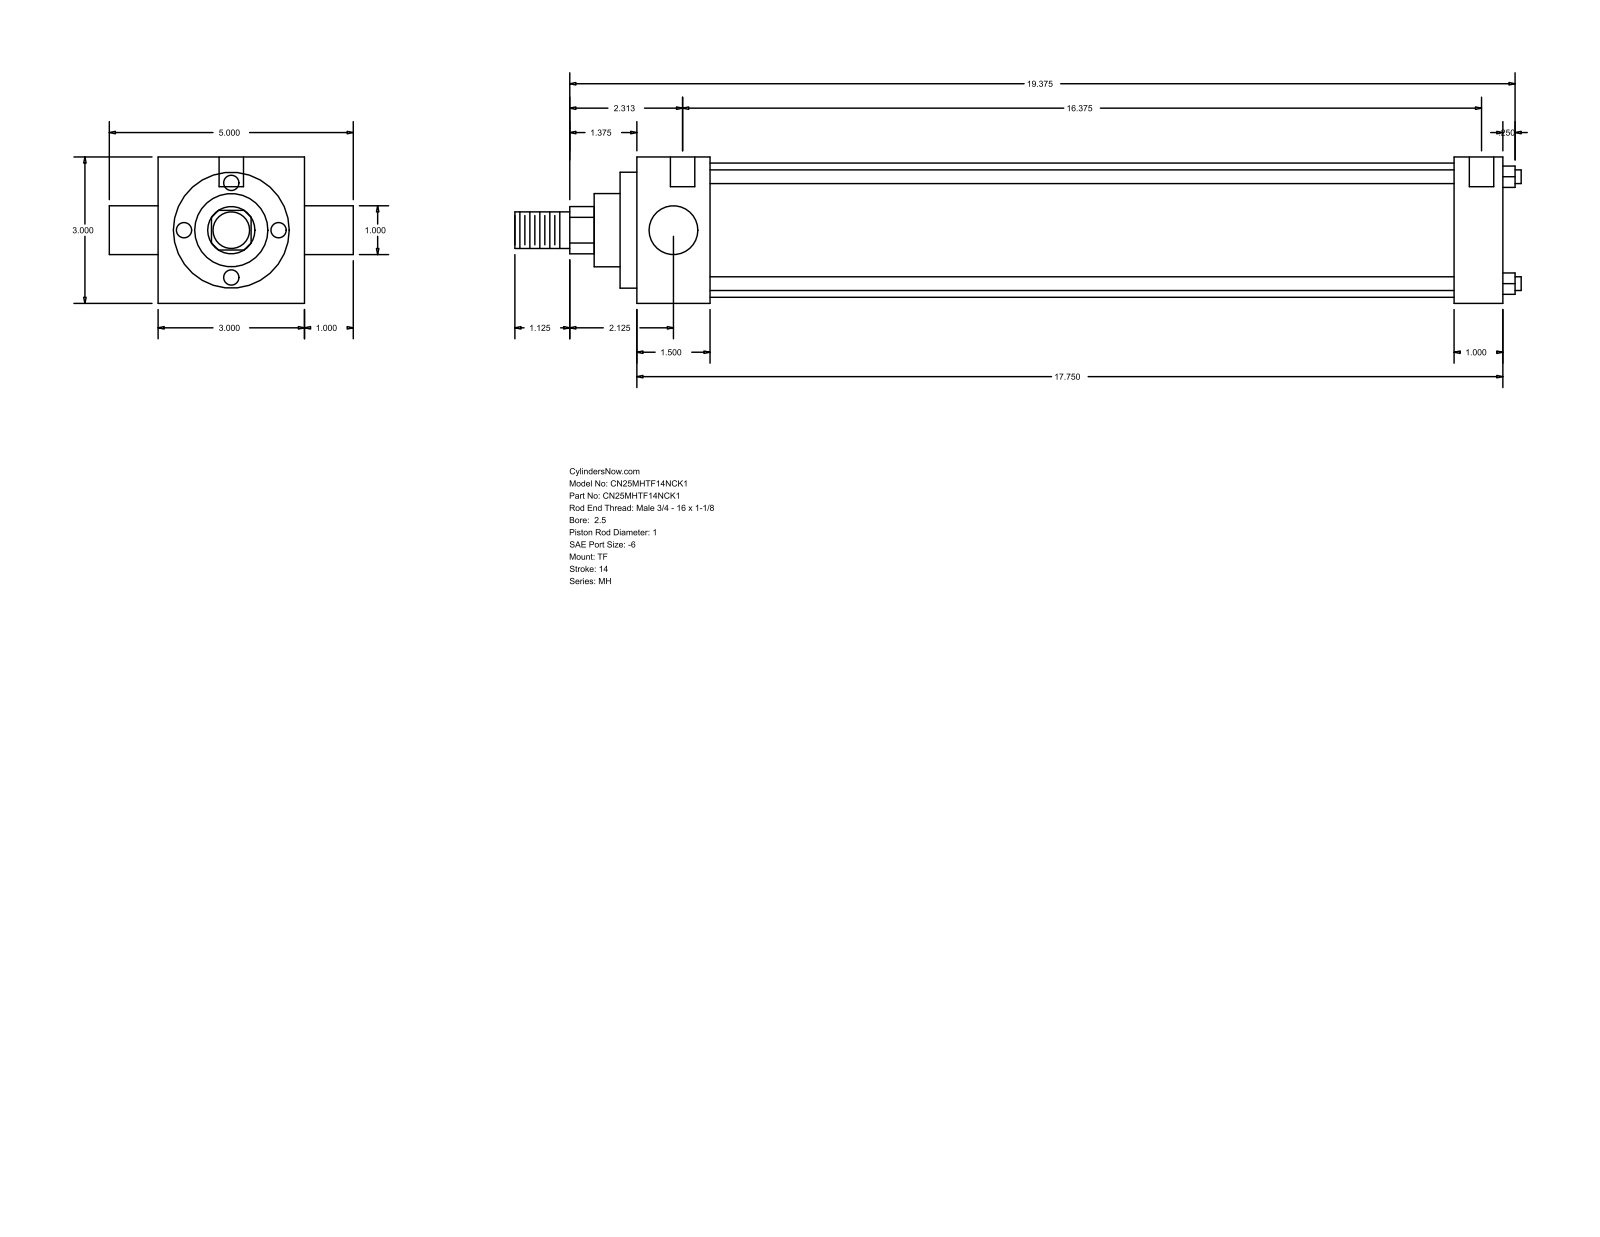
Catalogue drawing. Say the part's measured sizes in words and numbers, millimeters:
The part is named "MH_TF__0250_1". Its 3-D file was written by "GSSL Pune (CONFIG_CONTROL_DESIGN)". It is 0 solids with 86 faces: 61 planar, 25 cylindrical and 0 other. Overall it measures 523.88 by 127 by 76.2 millimeters. Round holes: 3 of diameter 5.56, 2 of diameter 12.7. Round bosses or shafts: 4 of diameter 7.14, 2 of diameter 25.4, 1 of diameter 69.85, 1 of diameter 60.33, 1 of diameter 38.1, 1 of diameter 19.05. Partial cylindrical surfaces (rounded edges, fillets, slot ends): 1 of radius 12.29. The main face-to-face distances are 76.2, 450.85, 25.39, 38.11, 412.74, 425.46, 387.35, 8.73, 46.84, 434.19. The hole center spacings are 3.18, 4.76, 415.92, 419.1, 420.68, 423.86.
